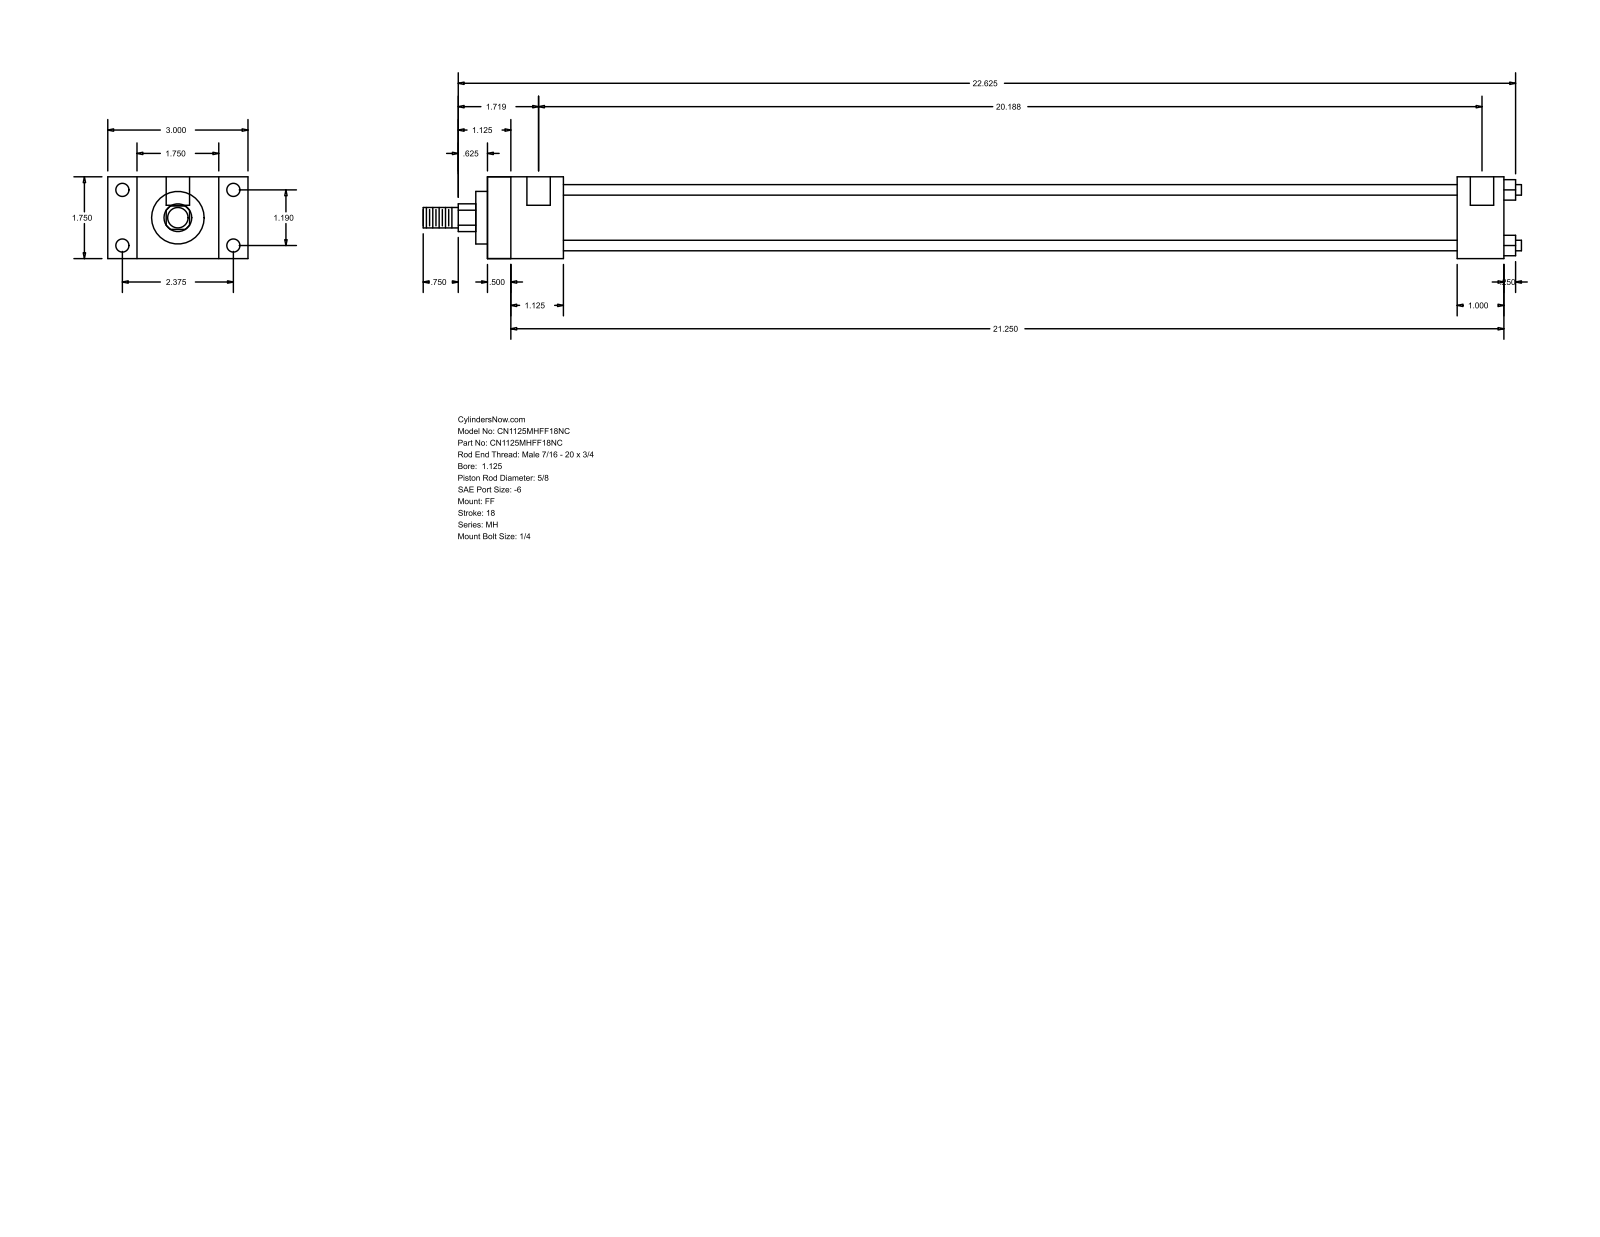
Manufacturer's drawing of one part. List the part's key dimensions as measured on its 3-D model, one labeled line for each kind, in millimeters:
Part name (STEP PRODUCT): MH_FF__0112_0.625
STEP written by: GSSL Pune (CONFIG_CONTROL_DESIGN)
Units: millimetres
Bodies: 0 solids, 92 faces (64 planar, 28 cylindrical, 0 other)
Overall size (bounding box): 596.9 × 76.2 × 44.45
Round holes (diameter × count): ⌀5.56 ×4, ⌀7.14 ×4, ⌀12.7 ×2
Round bosses / shafts (diameter × count): ⌀5.71 ×4, ⌀34.92 ×1, ⌀28.57 ×1, ⌀15.88 ×1, ⌀11.11 ×1
Partial cylindrical surfaces — rounded edges, fillets, slot ends (radius × count): R7.54 ×1
Main face-to-face distances: 44.46, 552.45, 15.87, 12.69, 539.76, 28.58, 60.33, 41.27, 527.04, 514.35
Hole centre spacings: 30.22, 60.32, 67.47, 509.59, 3.17, 512.76
